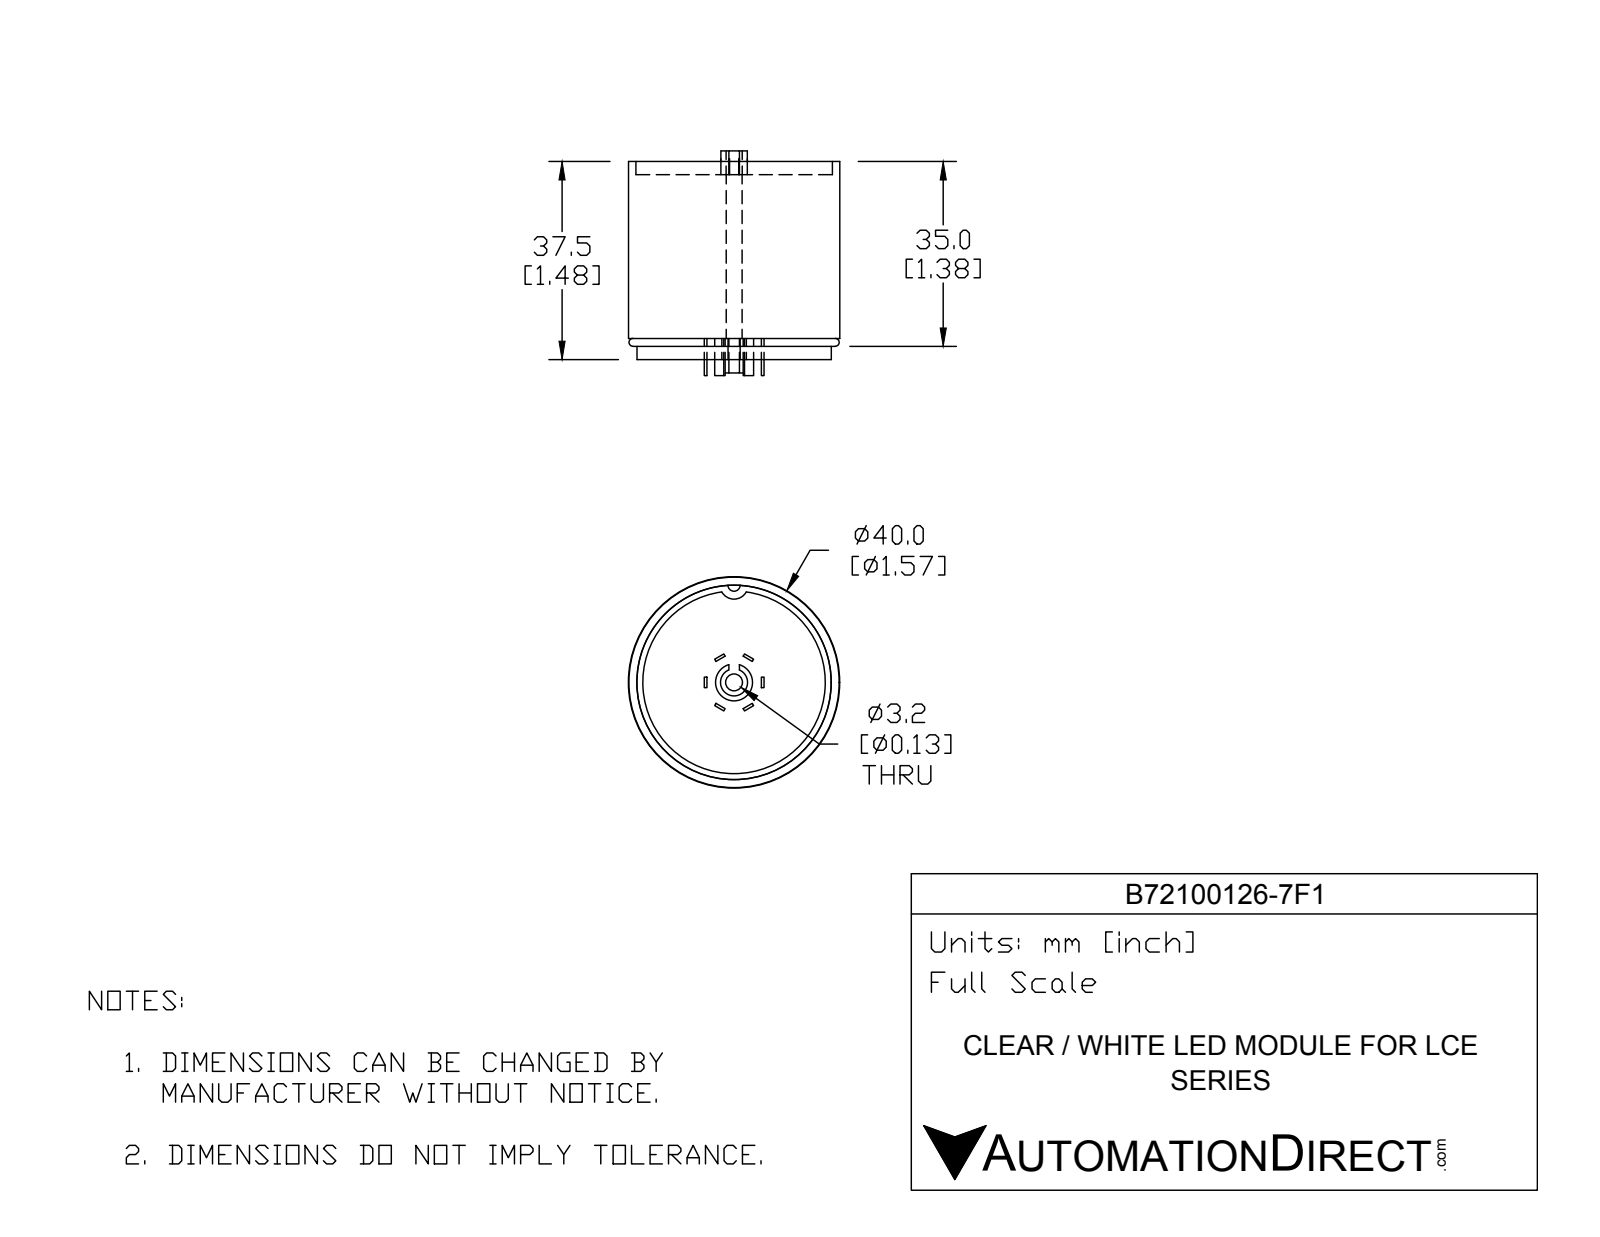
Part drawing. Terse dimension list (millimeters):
name: B72100126-7F1
written by: SolidWorks 2016 (AUTOMOTIVE_DESIGN)
unit: mm
bodies: 10 solids, 74 faces (50 planar, 20 cylindrical, 4 other)
size: 43.02 × 40 × 40
volume: 40 201 mm³; area: 9 548 mm²
holes: 1× ⌀3, 1× ⌀3.06, 1× ⌀5.1, 1× ⌀34.54, 1× ⌀37.2
bosses: 1× ⌀40, 1× ⌀36.8, 1× ⌀7, 1× ⌀5
rounds: 1× R0.9, 1× R1.15, 1× R2.65
face distances: 31, 34, 3, 4, 35, 38, 0.5, 10.8, 2, 11.3
